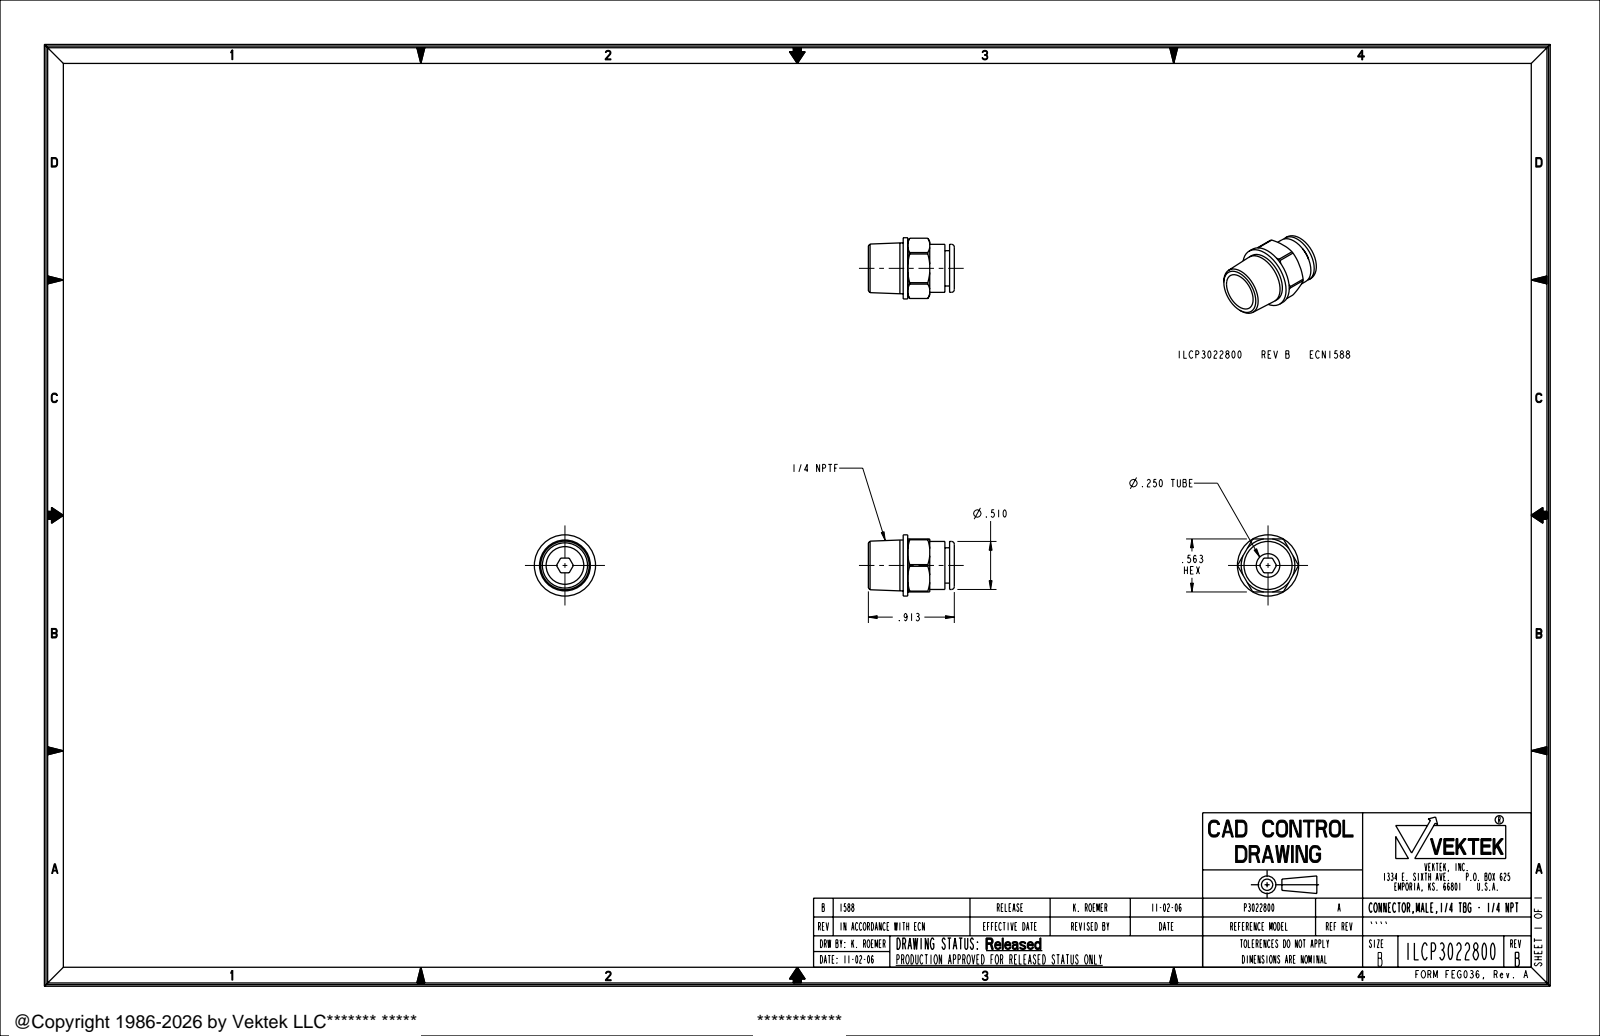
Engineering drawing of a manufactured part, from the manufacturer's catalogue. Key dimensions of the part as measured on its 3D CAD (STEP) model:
Part name (STEP PRODUCT): ILCP3022800
STEP written by: PRO/ENGINEER BY PARAMETRIC TECHNOLOGY CORPORATION, 2005180 (AUTOMOTIVE_DESIGN_CC2)
Units: inches
Bodies: 1 solid, 62 faces (22 planar, 22 cylindrical, 18 other)
Overall size (bounding box): 0.913 × 0.65 × 0.65
Volume: 0.14 in³ · Surface area: 3.237 in²
Round holes (diameter × count): ⌀0.25 ×1, ⌀0.4 ×1
Round bosses / shafts (diameter × count): ⌀0.65 ×1, ⌀0.54 ×1, ⌀0.51 ×1, ⌀0.375 ×1
Partial cylindrical surfaces — rounded edges, fillets, slot ends (radius × count): R0.32 ×1
Main face-to-face distances: 0.563, 0.05, 0.513, 0.495, 0.543, 0.018, 0.048, 0.03, 0.1, 0.395
